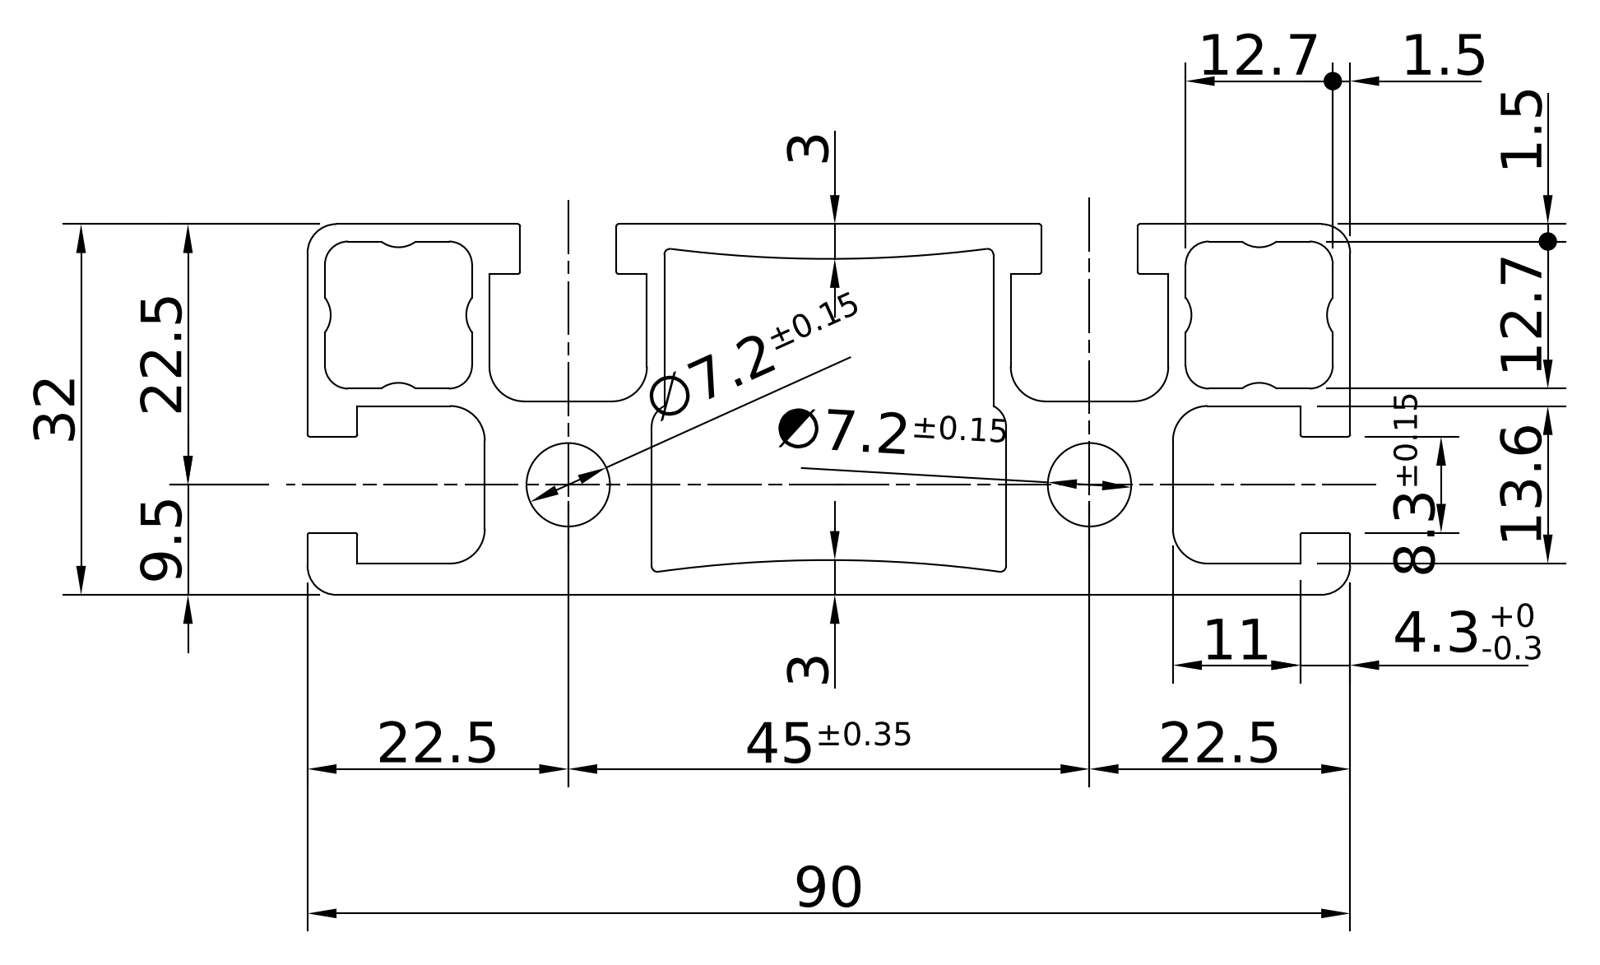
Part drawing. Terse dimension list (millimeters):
name: BPRDD0000925
written by: Autodesk Inventor 2019 (AUTOMOTIVE_DESIGN)
unit: mm
bodies: 1 solid, 112 faces (58 planar, 54 cylindrical, 0 other)
size: 100 × 90 × 32
volume: 97 368 mm³; area: 66 892 mm²
holes: 2× ⌀7.2
rounds: 16× R0.2, 12× R2.5, 10× R2, 8× R3, 4× R0.5, 2× R108.3
face distances: 32, 1.5, 1.1, 0.4, 14, 14.2, 29.3, 45, 15.1, 59.2
hole spacings: 45
